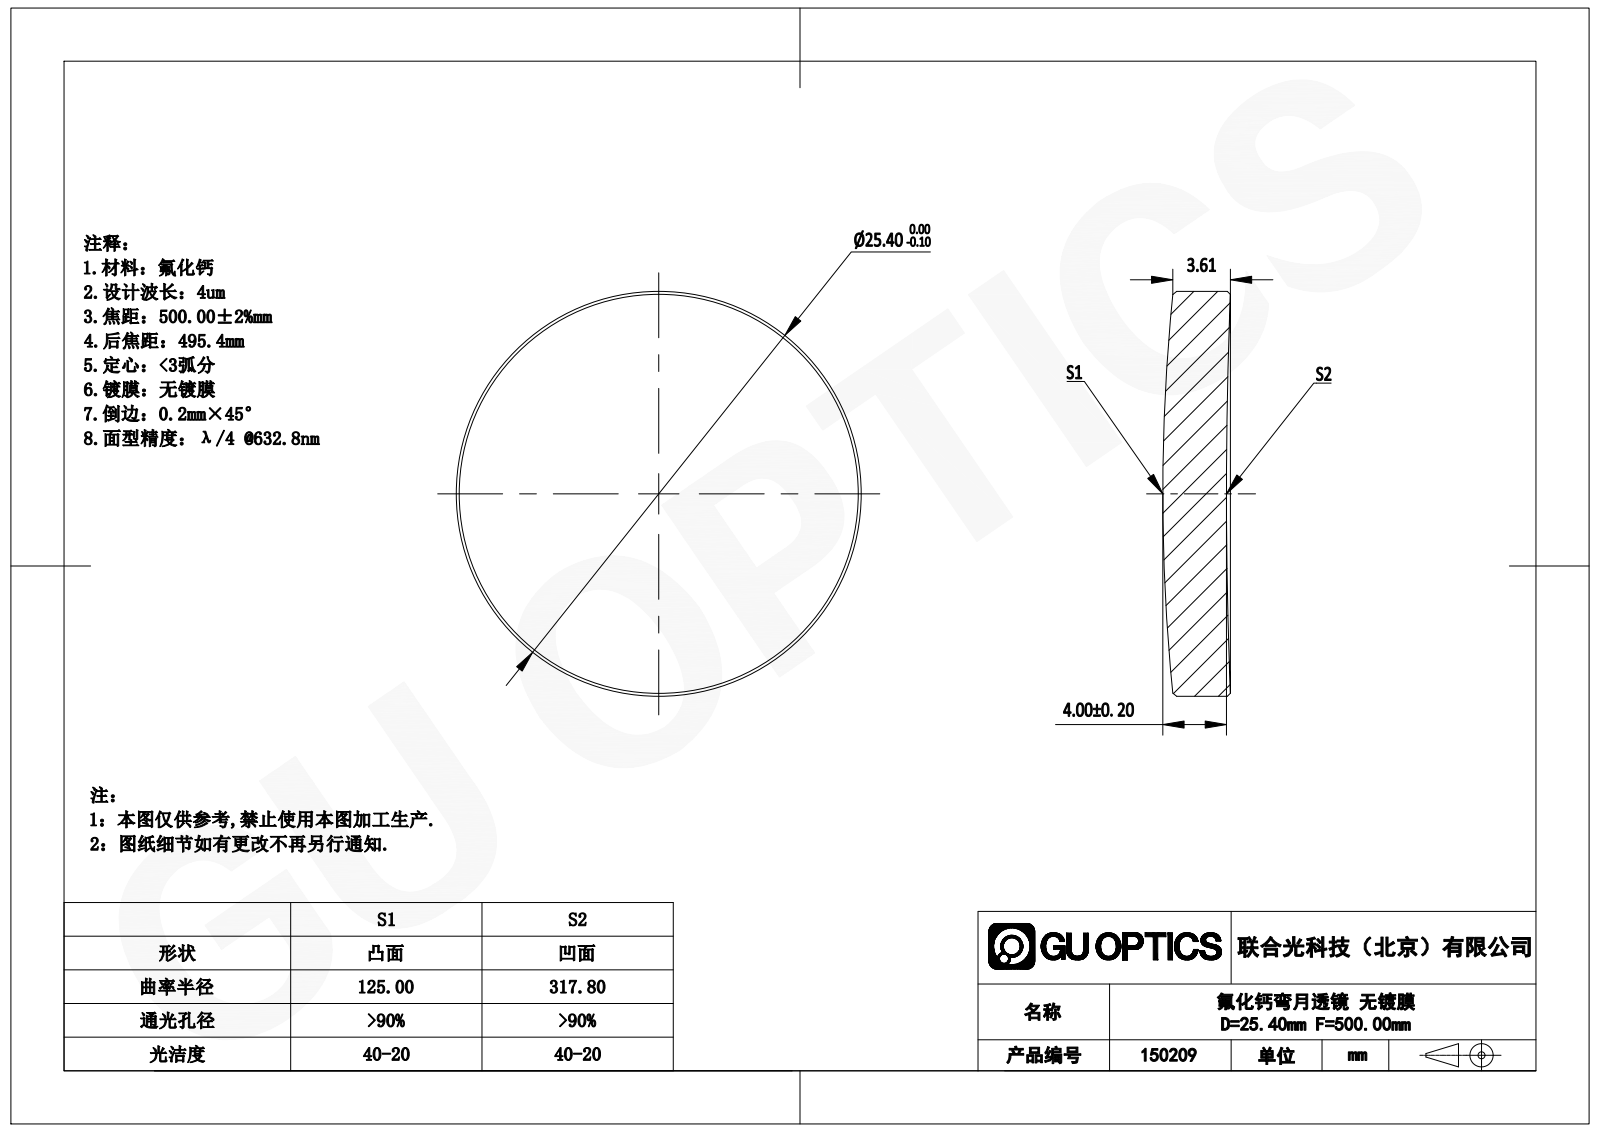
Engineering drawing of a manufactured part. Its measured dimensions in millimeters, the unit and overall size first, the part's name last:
Units: millimetres
Overall size (bounding box): 25.4 × 25.4 × 4.24
Round bosses / shafts (diameter × count): ⌀25.4 ×1
Volume: 1 921 mm³ · Surface area: 1 284 mm²
Bodies: 1 solid, 10 faces (0 planar, 2 cylindrical, 8 other)
Part name (STEP PRODUCT): GLM5-025B-500
STEP written by: SolidWorks 2022 (AUTOMOTIVE_DESIGN)
